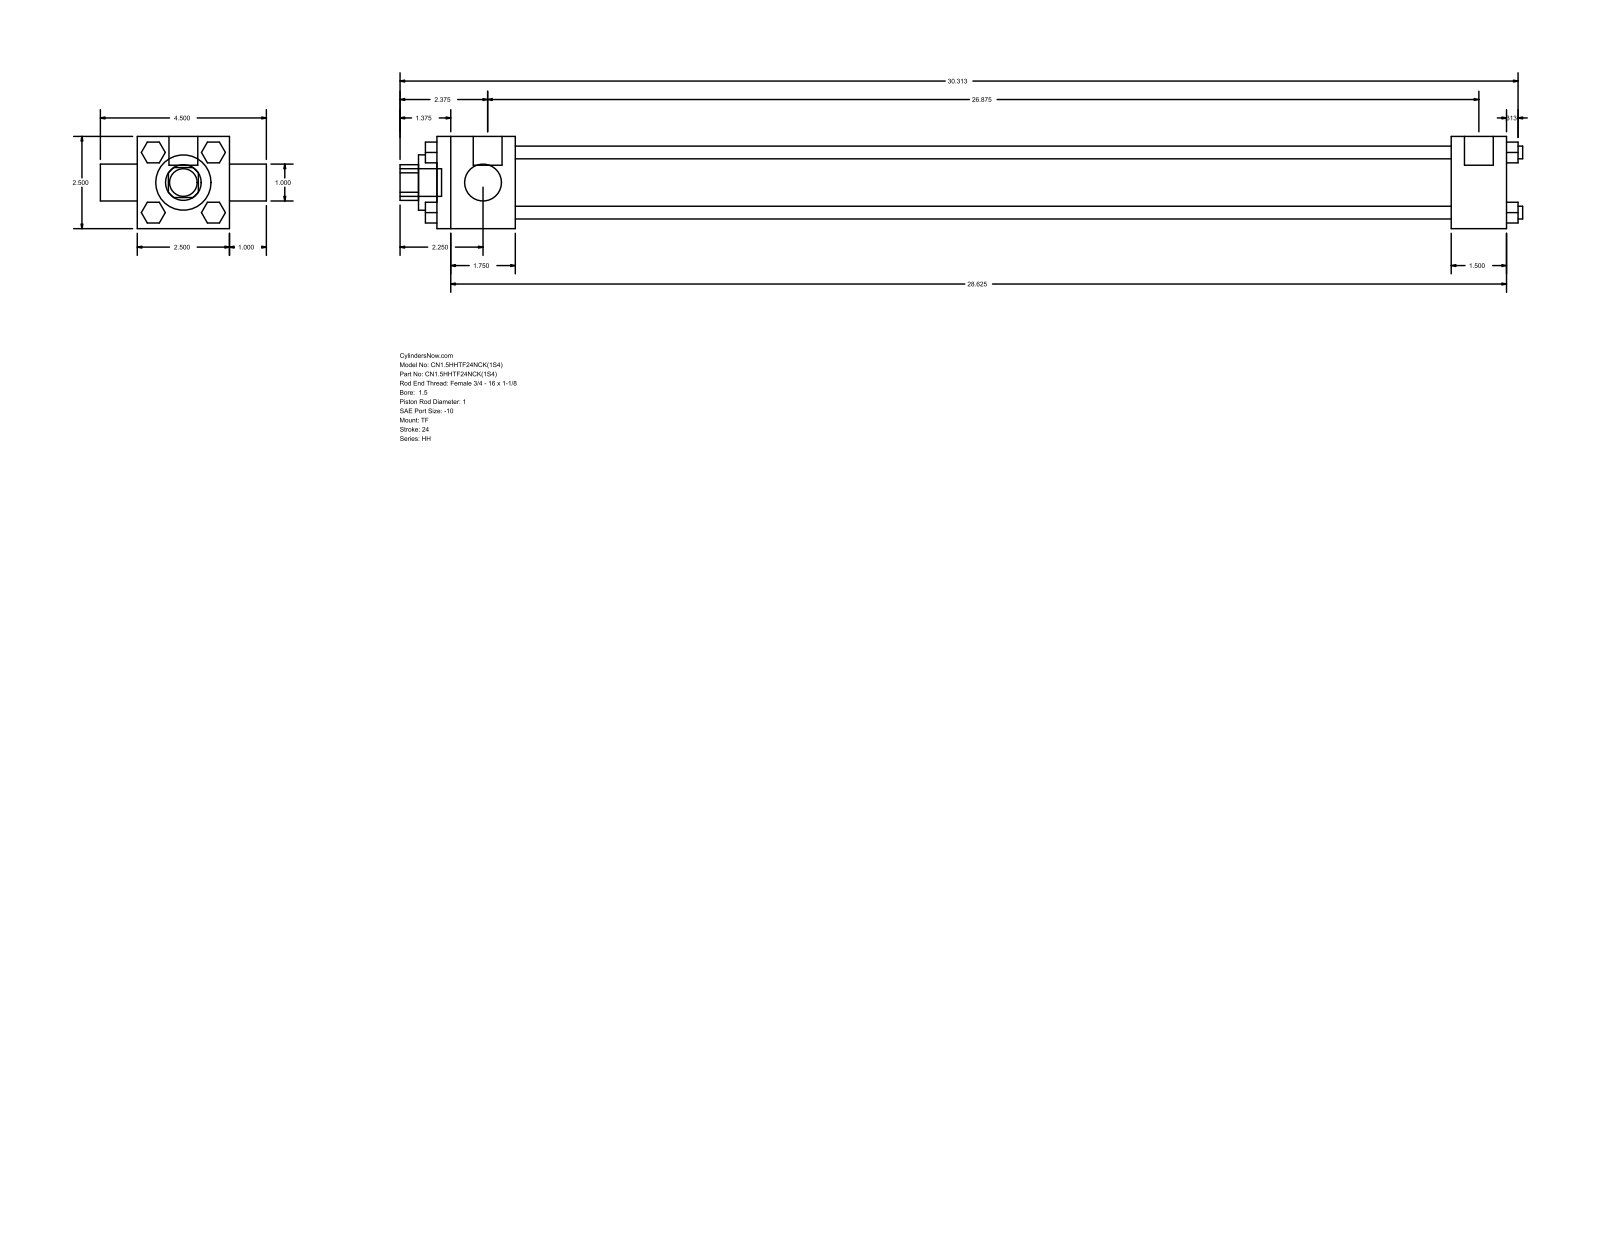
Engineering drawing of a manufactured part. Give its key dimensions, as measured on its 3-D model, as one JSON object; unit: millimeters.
{"part_name": "HH_TF__0150_1", "step_written_by": "GSSL Pune (CONFIG_CONTROL_DESIGN)", "units": "millimeters", "bodies": {"solids": 0, "faces": 120, "planar": 92, "cylindrical": 28, "other": 0}, "overall_size": [773.11, 114.3, 63.5], "round_holes": [[25.4, 2], [38.1, 1], [44.45, 1]], "round_bosses_or_shafts": [[8.76, 4], [5.56, 3], [19.84, 2], [19.05, 1]], "partial_cylinders_radius": [[12.29, 1]], "face_to_face_distances": [63.5, 682.62, 644.52, 38.1, 53.98, 698.5, 736.6, 744.54, 25.4, 20.7]}
